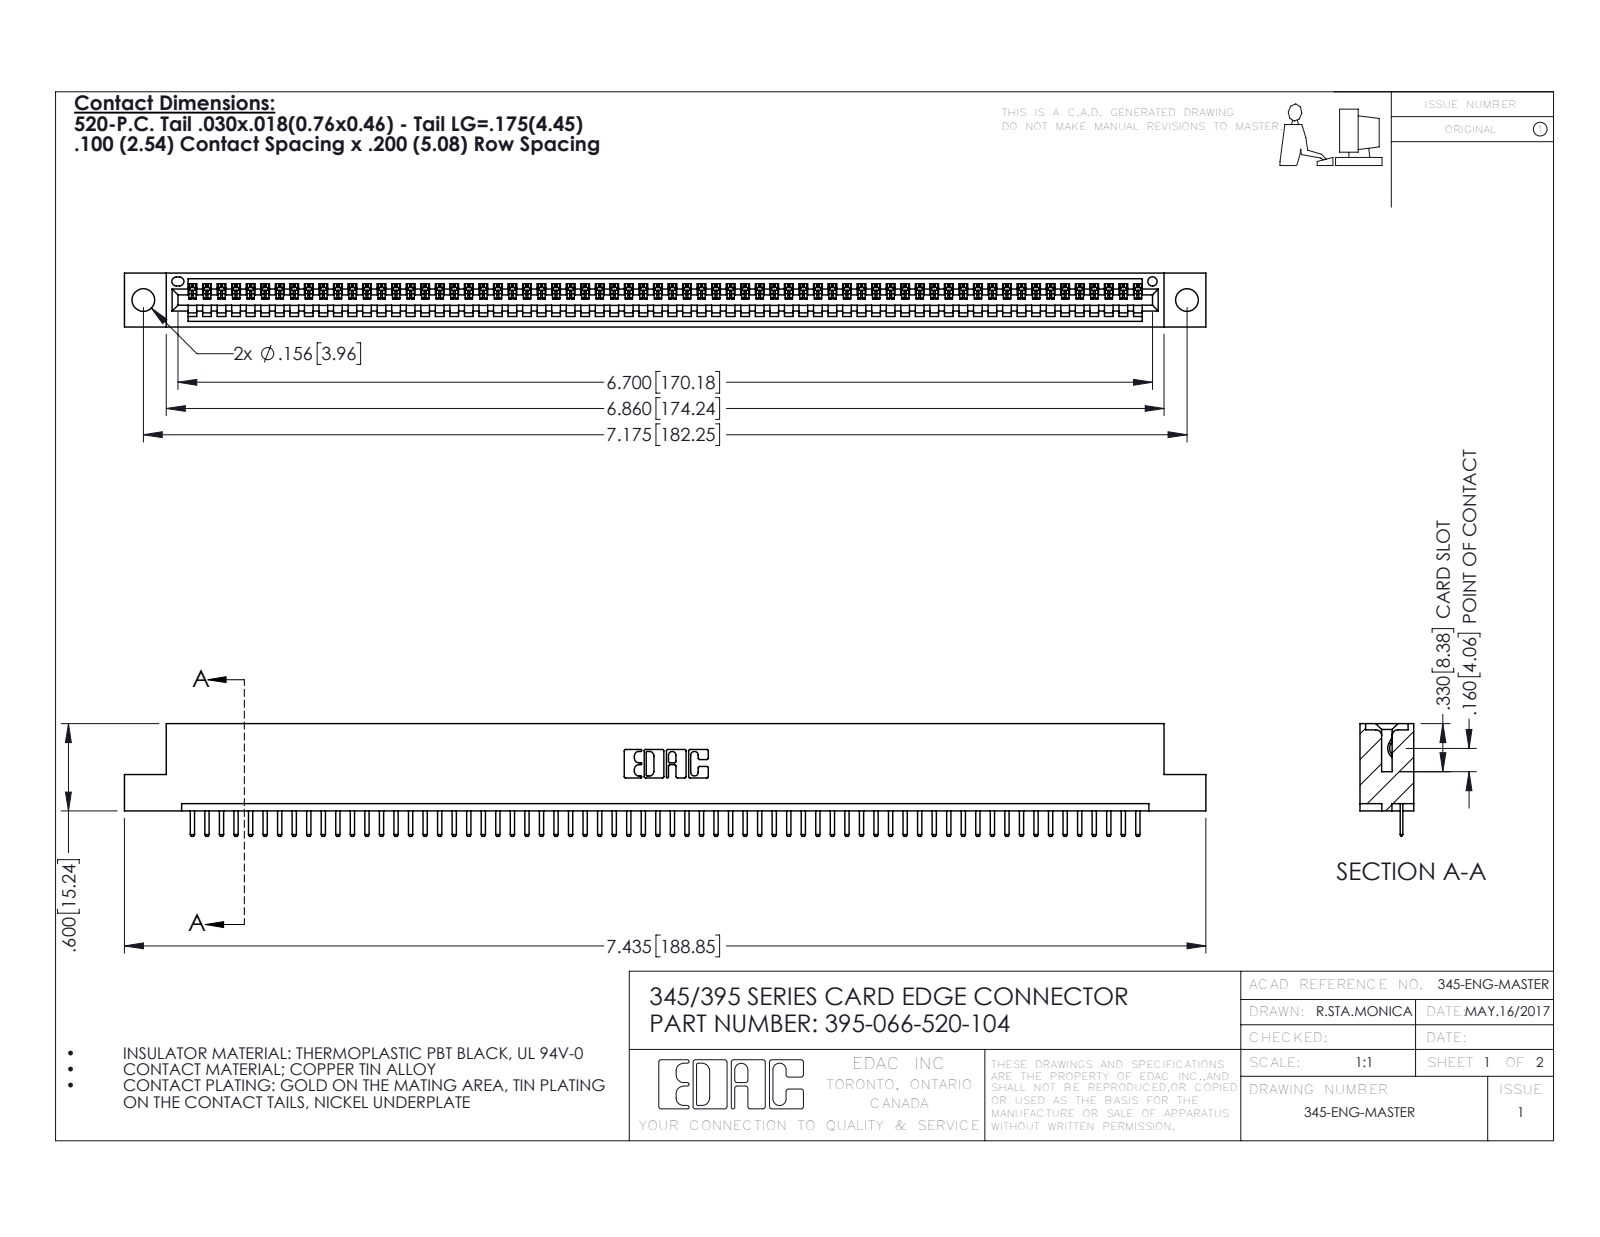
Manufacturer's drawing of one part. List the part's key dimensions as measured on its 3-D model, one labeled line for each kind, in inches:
Part name (STEP PRODUCT): 395-066-520-104; 345-292-001_345-293-120; 345 Part_Flush Mounting Lugs - 0.156 Dia-TH
STEP written by: SolidWorks 2016 (CONFIG_CONTROL_DESIGN)
Units: inches
Bodies: 67 solids, 4218 faces (2852 planar, 1366 cylindrical, 0 other)
Overall size (bounding box): 7.435 × 0.775 × 0.37
Volume: 1.09 in³ · Surface area: 36.03 in²
Round holes (diameter × count): ⌀0.156 ×2, ⌀0.064 ×1
Partial cylindrical surfaces — rounded edges, fillets, slot ends (radius × count): R0.01 ×134, R0.006 ×132, R0.01 ×22, R0.007 ×6, R0.031 ×6, R0.026 ×3, R0.031 ×2, R0.04 ×2
Main face-to-face distances: 0.298, 0.072, 0.37, 0.2, 0.098, 0.272, 0.025, 0.225, 0.072, 0.149
Hole centre spacings: 0.27, 6.939, 7.175
